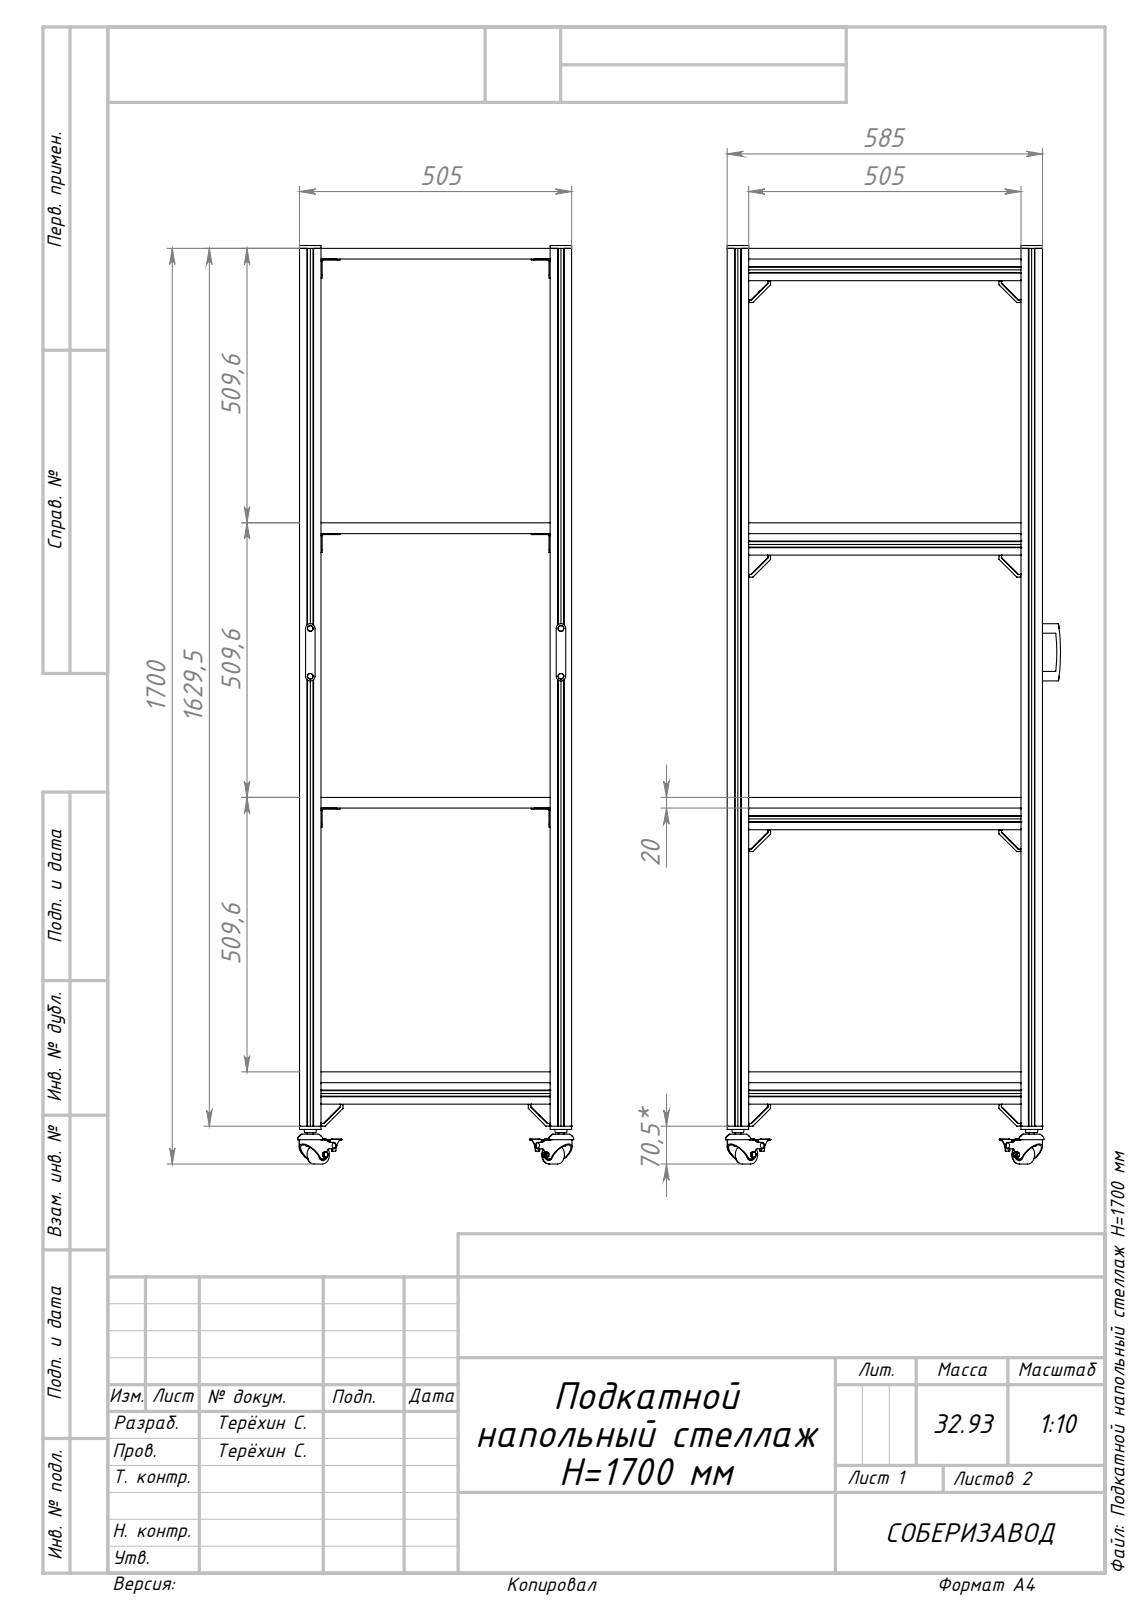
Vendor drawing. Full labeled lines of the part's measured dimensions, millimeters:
Part name (STEP PRODUCT): A19_00; A18_01; E36_00; T28_00 (+8 more)
STEP written by: SolidWorks 2021 (AUTOMOTIVE_DESIGN)
Units: millimetres
Bodies: 126 solids, 11590 faces (6308 planar, 4454 cylindrical, 828 other)
Overall size (bounding box): 1705.3 × 621.54 × 512.45
Volume: 27 470 000 mm³ · Surface area: 8 632 000 mm²
Round holes (diameter × count): ⌀4 ×32, ⌀1.7 ×16, ⌀6 ×14, ⌀8.1 ×12, ⌀4.8 ×8, ⌀5 ×8, ⌀10 ×8, ⌀6.2 ×4, ⌀8.5 ×4, ⌀10.5 ×4, ⌀12 ×4, ⌀22 ×4
Round bosses / shafts (diameter × count): ⌀20 ×8, ⌀5.7 ×8, ⌀35 ×4, ⌀17.7 ×4, ⌀16 ×4, ⌀10 ×4, ⌀5 ×4
Partial cylindrical surfaces — rounded edges, fillets, slot ends (radius × count): R1 ×1384, R0.25 ×1088, R0.3 ×336, R0.35 ×112, R0.6 ×112, R0.8 ×112, R0.1 ×80, R2 ×64
Main face-to-face distances: 509.6, 1019.2, 20, 529.6, 489.6, 465, 40, 1528.8, 29, 11
Hole centre spacings: 672.38, 545, 672.41, 11.6, 18.83, 18.92, 10.64, 16.89
